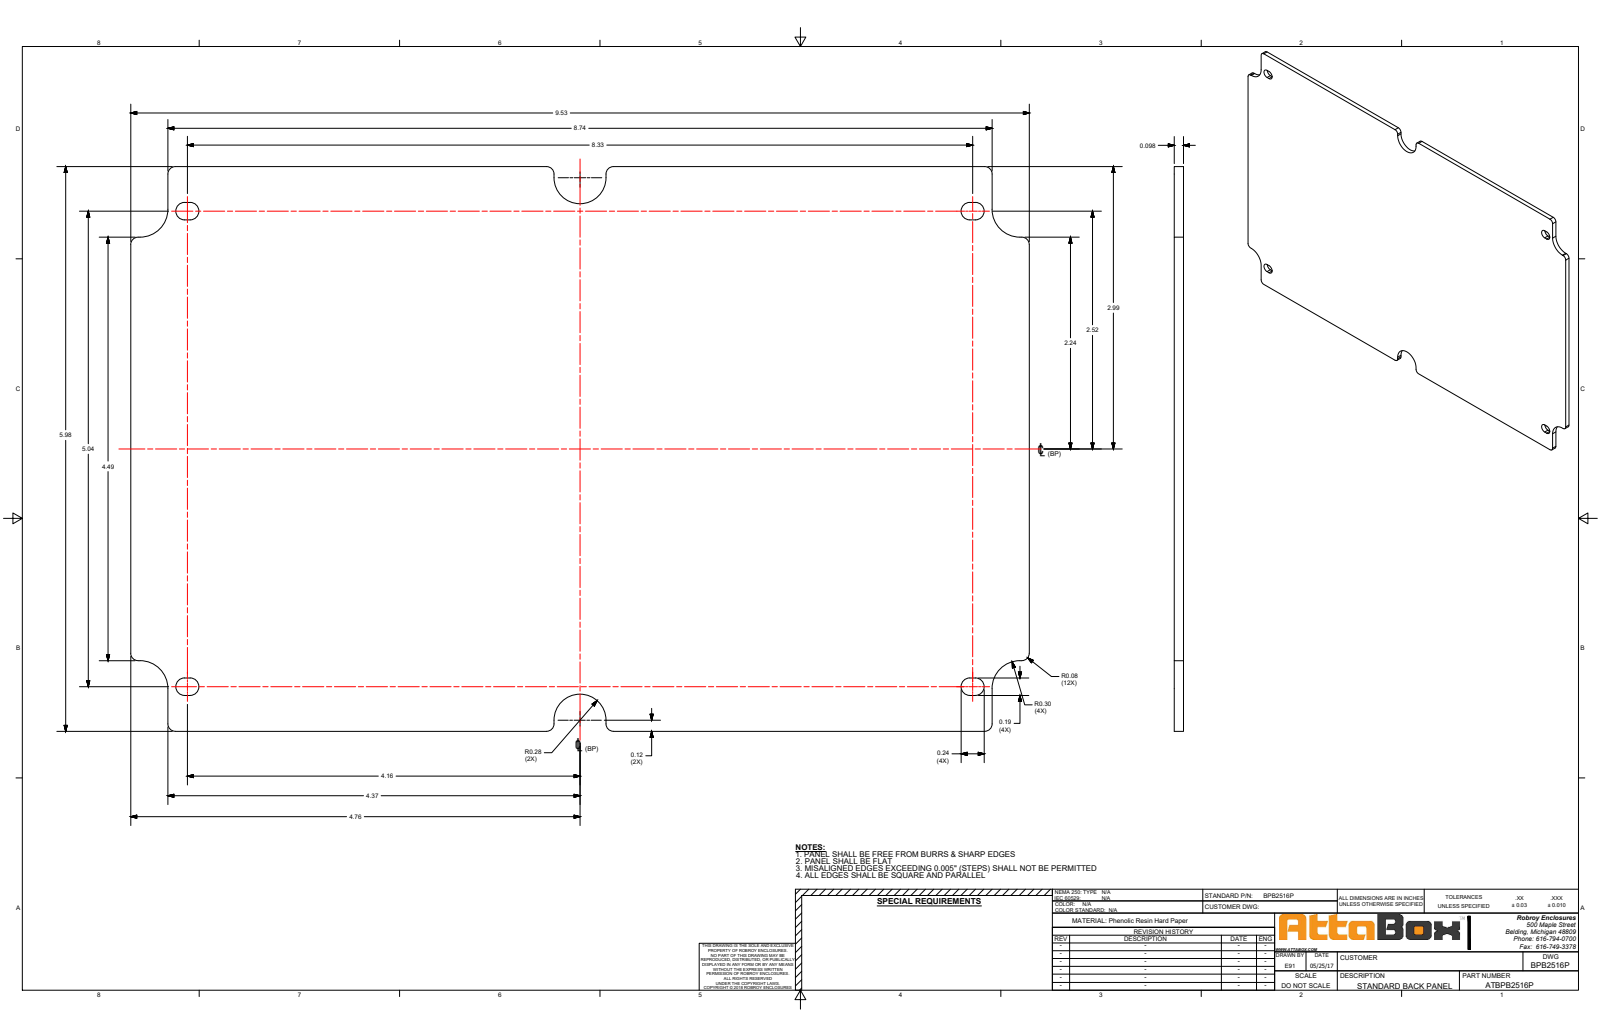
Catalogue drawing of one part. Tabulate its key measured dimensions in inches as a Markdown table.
| quantity | value |
| --- | --- |
| part name | BPB2516P |
| STEP written by | SolidWorks 2018 (AUTOMOTIVE_DESIGN) |
| units | inches |
| bodies | 1 solid, 54 faces (28 planar, 26 cylindrical, 0 other) |
| overall size | 9.528 × 5.984 × 0.098 |
| volume | 5.45 in³ |
| surface area | 114.1 in² |
| partial cylindrical surfaces (radius × count) | 0.079 × 12, 0.093 × 8, 0.295 × 4, 0.276 × 2 |
| main face-to-face distances | 0.098, 5.984, 9.528, 0.394, 9.134, 8.74, 5.039, 0.565, 5.419, 0.38 |
